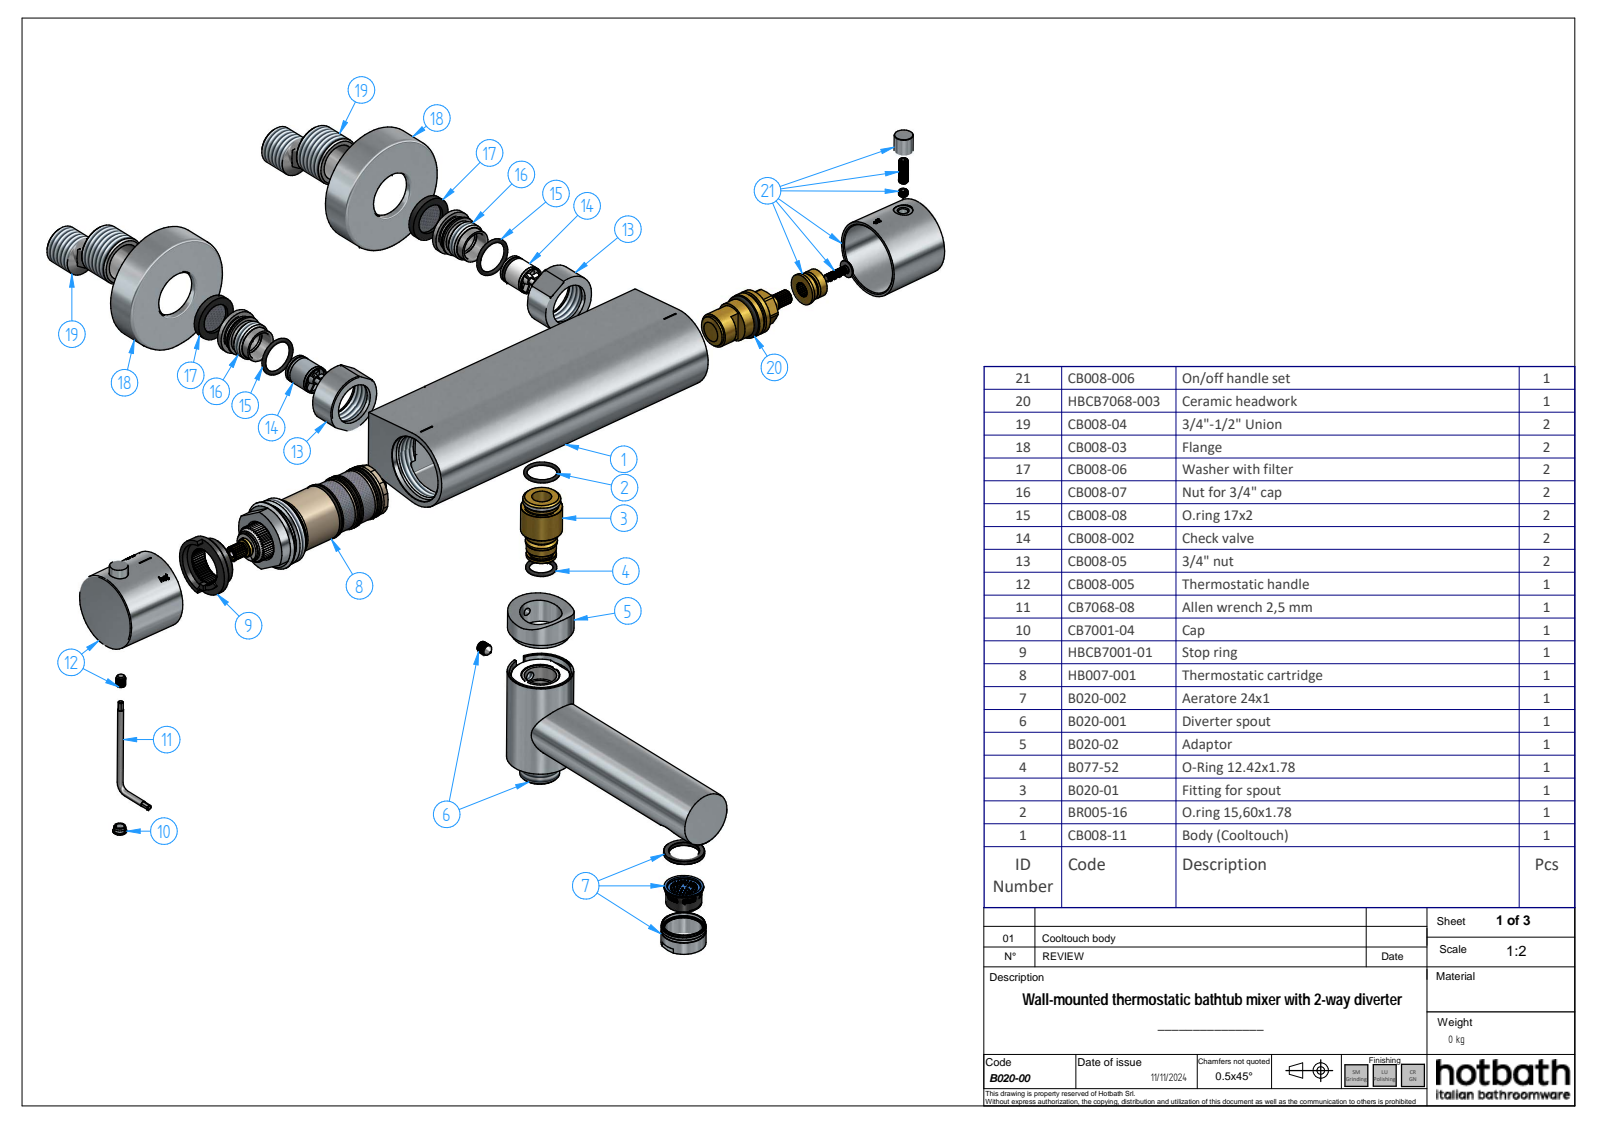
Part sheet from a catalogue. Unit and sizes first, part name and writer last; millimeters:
Units: millimetres
Overall size (bounding box): 259.35 × 199.01 × 127.2
Round holes (diameter × count): ⌀10.2 ×3, ⌀18.5 ×3, ⌀21 ×3, ⌀22.2 ×3, ⌀25 ×3, ⌀3 ×2, ⌀3.5 ×2, ⌀4.13 ×2, ⌀5.2 ×2, ⌀15.05 ×2, ⌀15.8 ×2, ⌀24.12 ×2
Round bosses / shafts (diameter × count): ⌀0.24 ×26, ⌀64 ×2, ⌀24 ×2, ⌀21.7 ×2, ⌀20 ×2, ⌀19.2 ×2, ⌀18.05 ×2, ⌀18 ×2
Partial cylindrical surfaces — rounded edges, fillets, slot ends (radius × count): R2 ×118, R0.5 ×7, R0.2 ×6, R3 ×5, R0.3 ×4, R1.99 ×2, R2.1 ×2, R3.5 ×2
Main face-to-face distances: 4, 0.5, 3.5, 18, 20.5, 17, 16.5, 21, 17.5, 3
Hole centre spacings: 5, 34.1, 79.25, 92.83, 2, 9.11, 11.89, 11.9
Volume: 283 215 mm³ · Surface area: 190 165 mm²
Bodies: 19 solids, 4538 faces (470 planar, 3603 cylindrical, 465 other)
Part name (STEP PRODUCT): B020-00 Rel1; CB008-07; CB008-03; CB008-05 (+8 more)
STEP written by: Solid Edge (AUTOMOTIVE_DESIGN)
